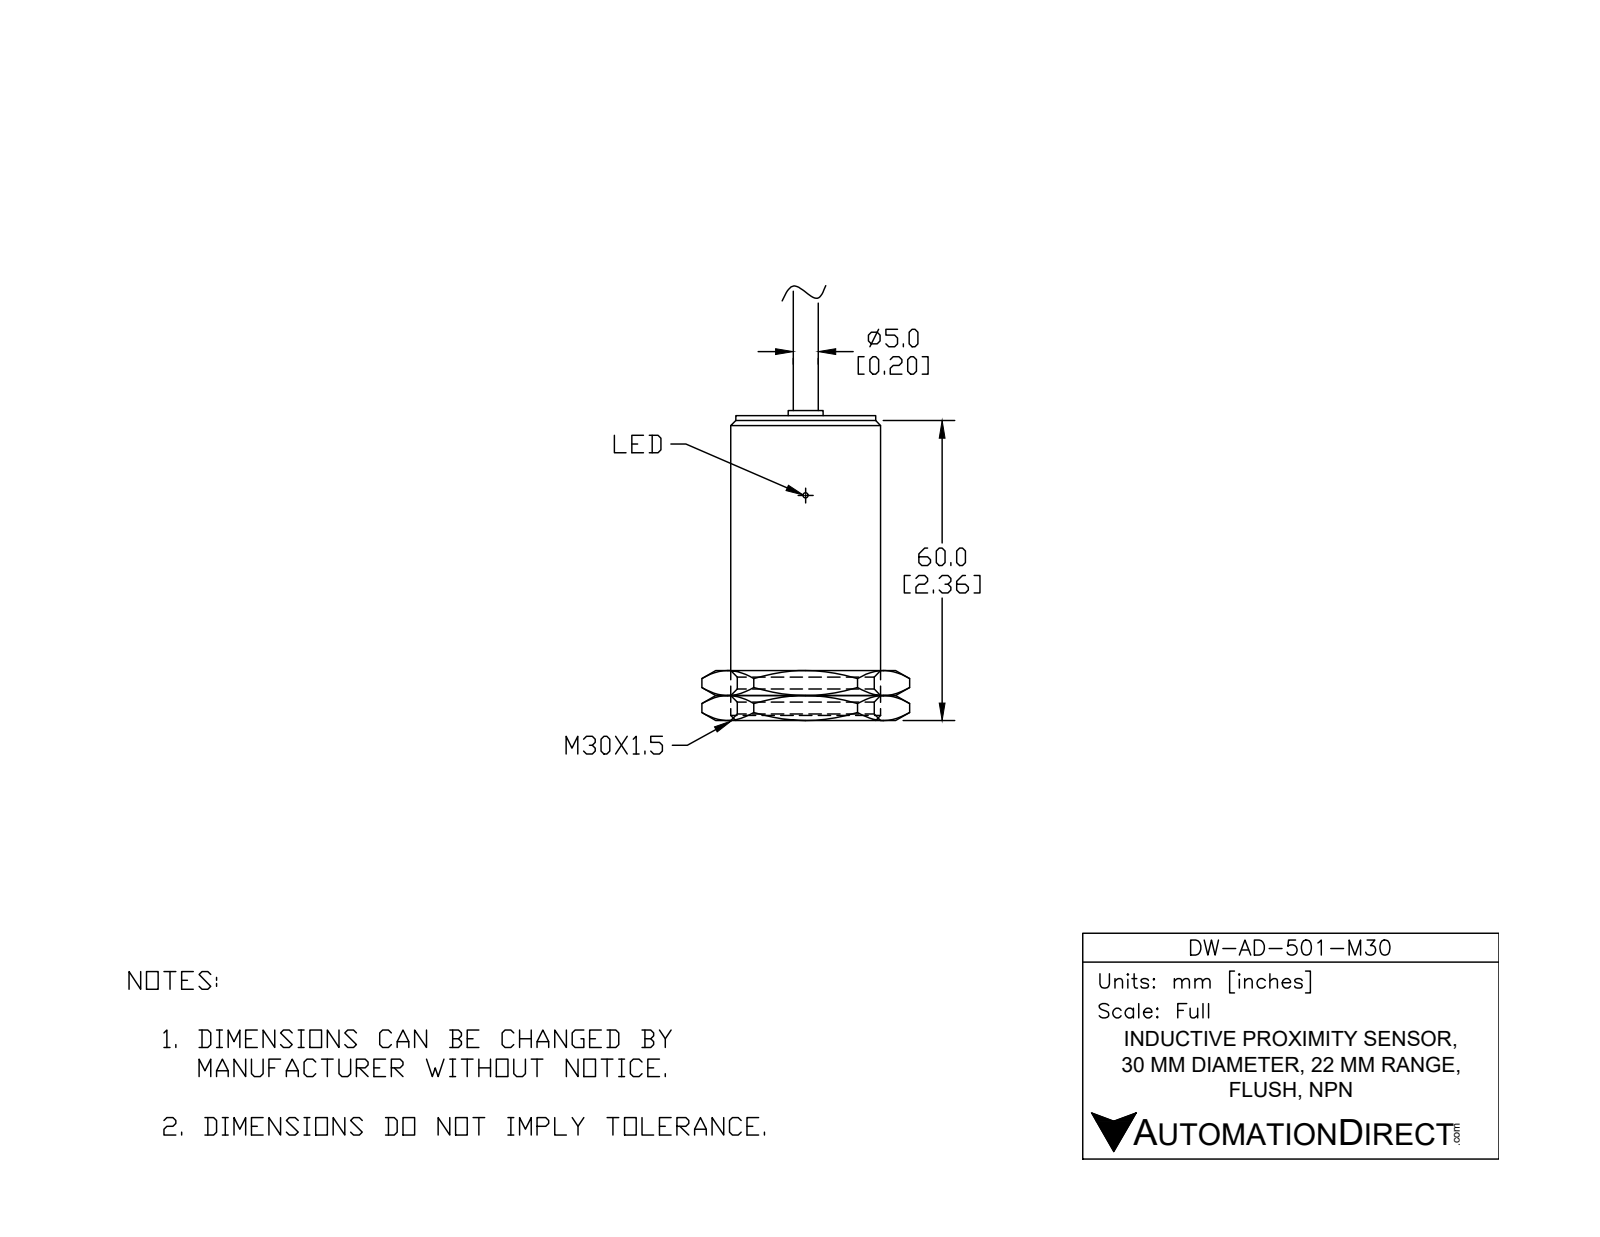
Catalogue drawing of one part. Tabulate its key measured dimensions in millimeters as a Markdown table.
| quantity | value |
| --- | --- |
| part name | DW-AD-501-M30 |
| STEP written by | SolidWorks 2017 (AUTOMOTIVE_DESIGN) |
| units | millimeters |
| bodies | 2 solids, 31 faces (17 planar, 5 cylindrical, 9 other) |
| overall size | 86.6 × 30 × 30 |
| volume | 43 560 mm³ |
| surface area | 7 535 mm² |
| round bosses / shafts (diameter × count) | 30 × 1, 27.5 × 1, 10.5 × 1, 6.8 × 1, 5 × 1 |
| main face-to-face distances | 61, 63, 2, 0.8, 61.8, 1.2, 58, 3, 3.8, 5 |
